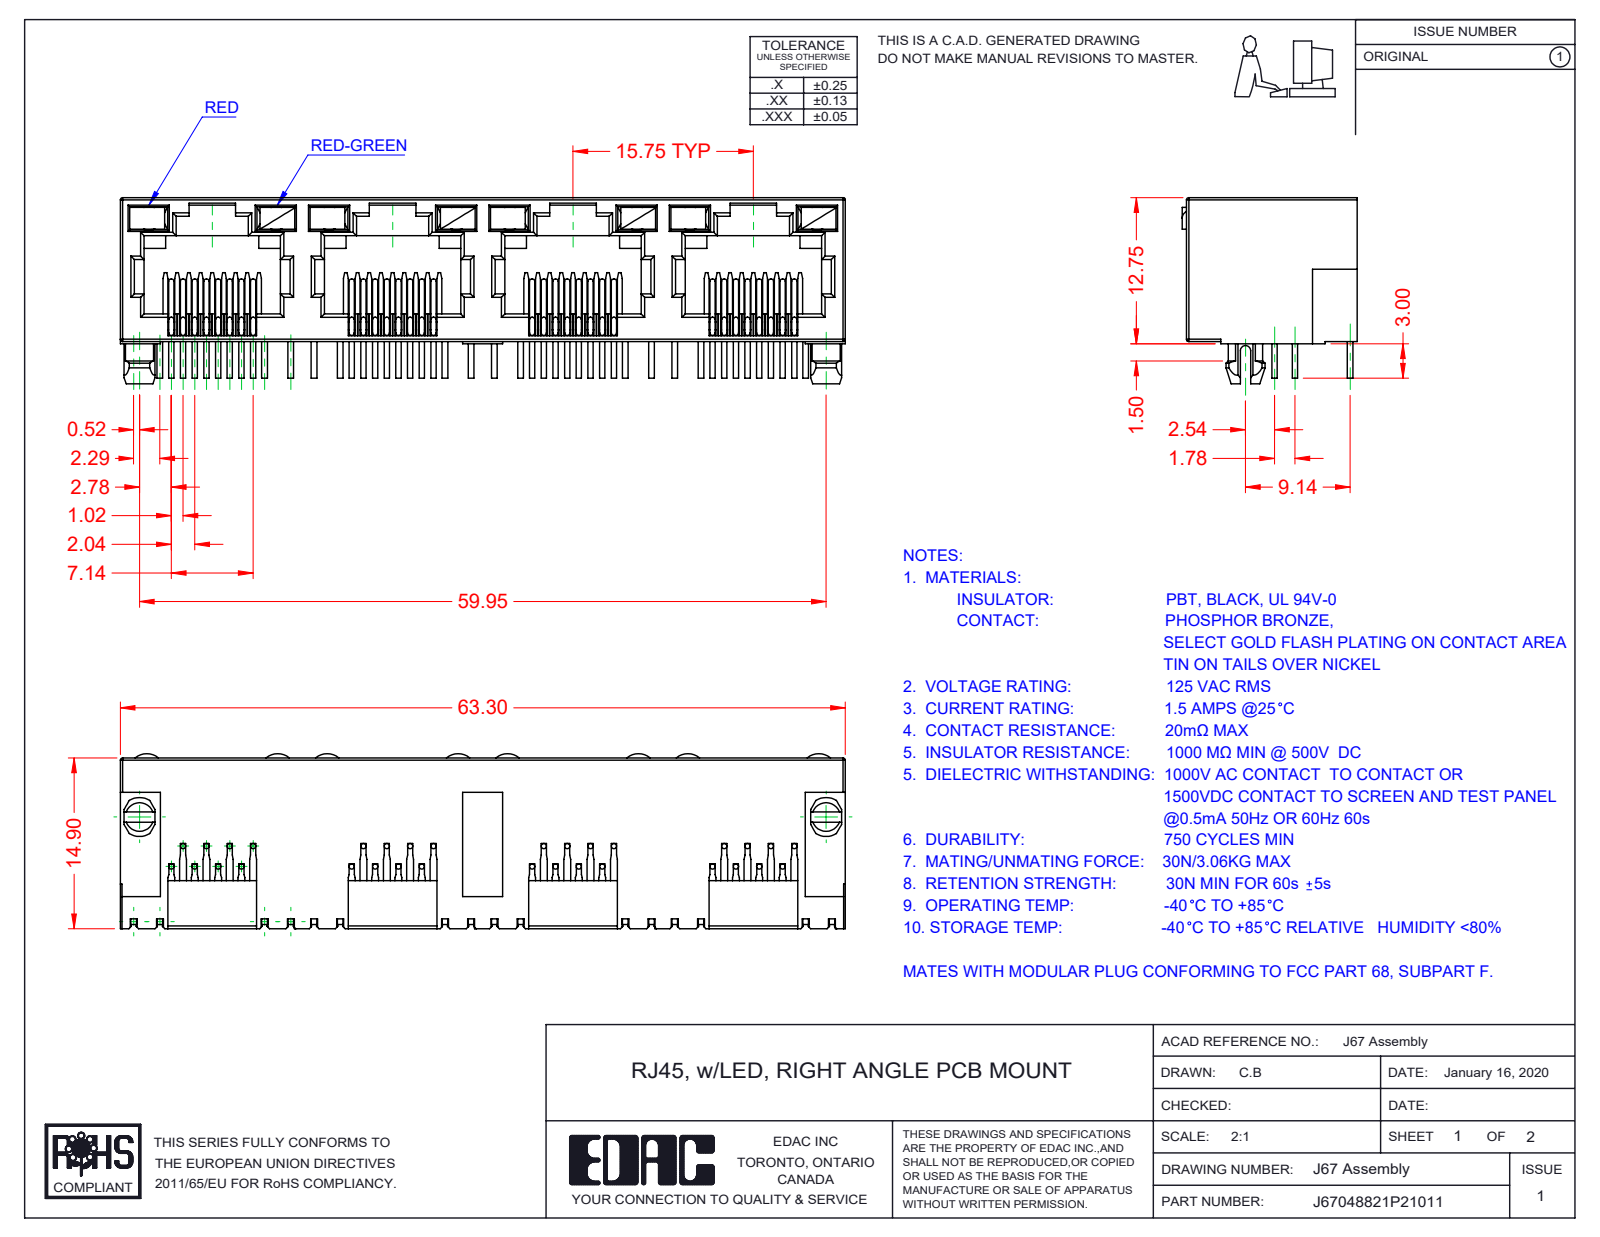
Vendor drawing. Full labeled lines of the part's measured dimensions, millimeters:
Part name (STEP PRODUCT): 67 Contacts; 67 LED RH_6-Red-Green; J67048822P26011; 67 Insulator (+1 more)
STEP written by: SolidWorks 2016 (CONFIG_CONTROL_DESIGN)
Units: millimetres
Bodies: 41 solids, 2473 faces (1781 planar, 484 cylindrical, 208 other)
Overall size (bounding box): 63.3 × 16.25 × 15.28
Volume: 5 159 mm³ · Surface area: 11 573 mm²
Round bosses / shafts (diameter × count): ⌀0.46 ×96
Partial cylindrical surfaces — rounded edges, fillets, slot ends (radius × count): R0.2 ×66, R0.3 ×29, R0.45 ×9, R1.55 ×8, R1.5 ×2, R1.7 ×2, R0.35 ×1, R1 ×1
Main face-to-face distances: 0.5, 12.55, 1.89, 0.89, 10, 15.75, 1, 1.39, 11, 11.89
